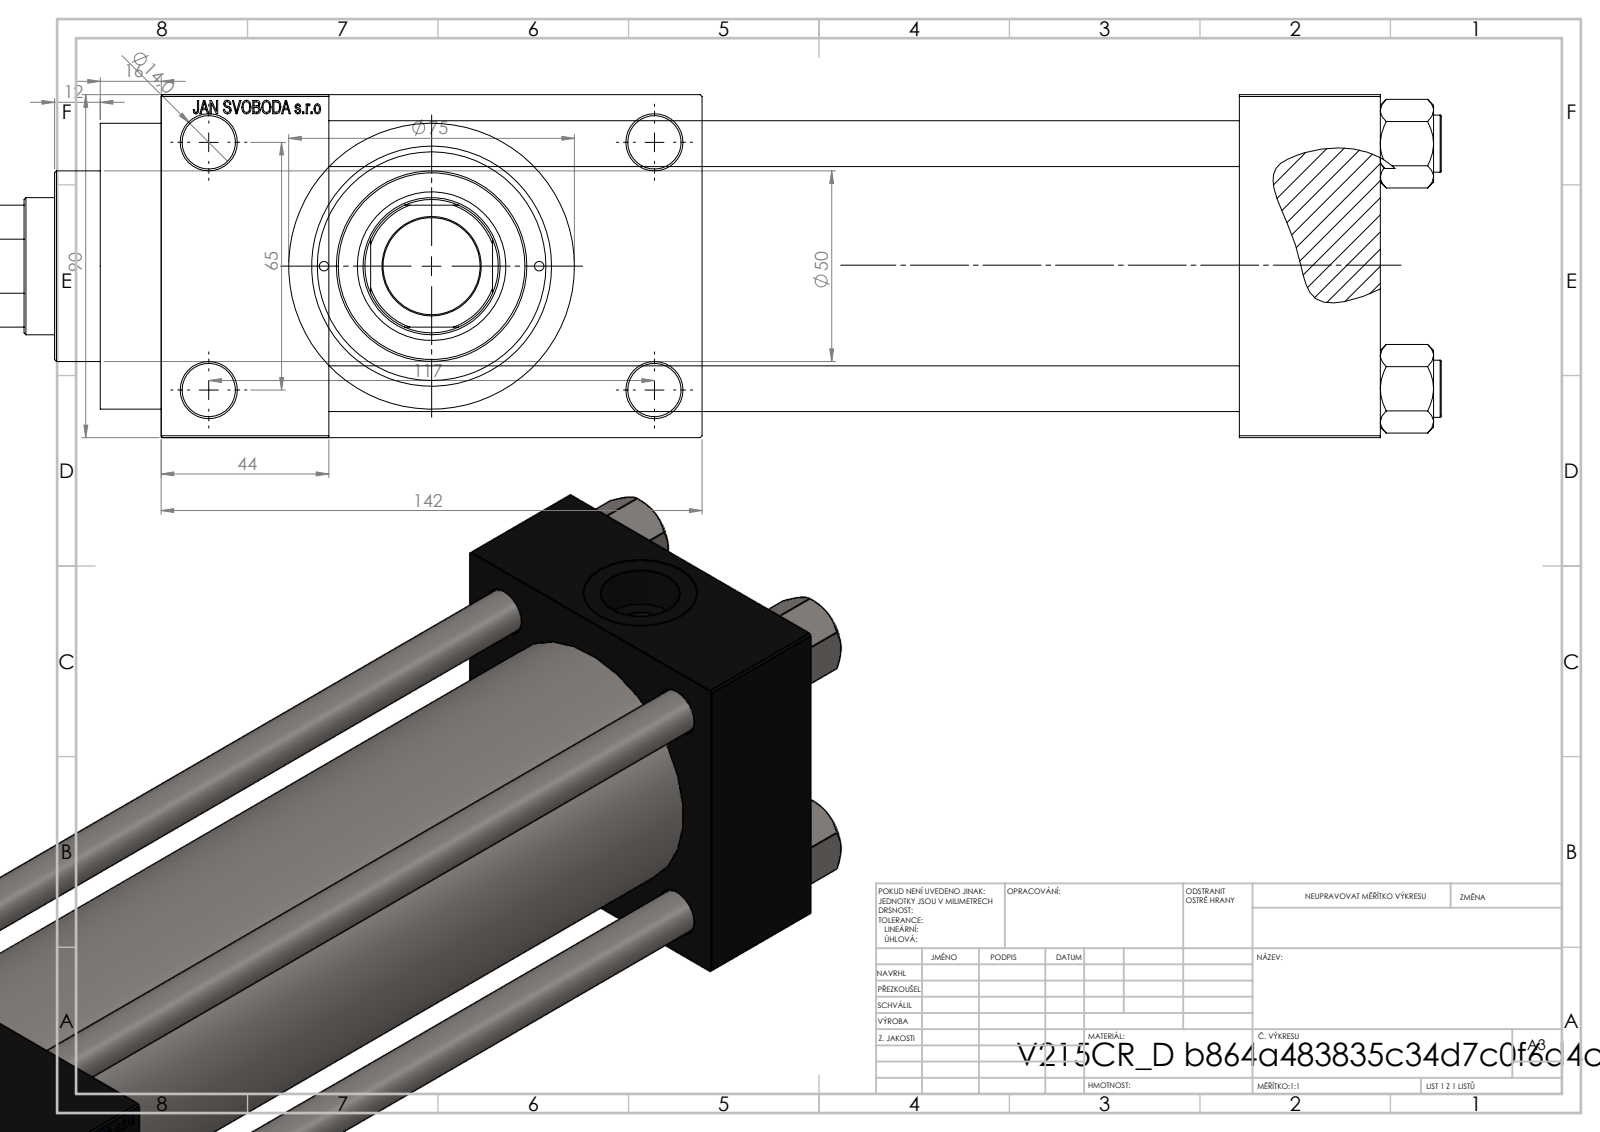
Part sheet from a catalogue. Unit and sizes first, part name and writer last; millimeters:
Units: millimetres
Overall size (bounding box): 383 × 142 × 90
Round holes (diameter × count): ⌀12 ×4, ⌀14 ×4, ⌀2.5 ×2, ⌀7 ×2, ⌀20.96 ×2, ⌀30 ×2, ⌀25.5 ×1, ⌀36 ×1, ⌀39 ×1, ⌀50 ×1, ⌀60 ×1, ⌀63 ×1
Round bosses / shafts (diameter × count): ⌀15 ×4, ⌀75 ×1, ⌀69 ×1
Partial cylindrical surfaces — rounded edges, fillets, slot ends (radius × count): R17.5 ×1
Main face-to-face distances: 90, 239, 37, 276, 320, 283, 44, 26, 116, 142
Hole centre spacings: 26.35, 32.39, 44.4, 45.47, 64.3, 66.92, 68.42, 69.81
Volume: 1 488 000 mm³ · Surface area: 327 850 mm²
Bodies: 11 solids, 1112 faces (499 planar, 93 cylindrical, 520 other)
Part name (STEP PRODUCT): NUT_M5_D; V215_VC_A; V215CR_D_TYCINKA; V215CR_D_Body (+1 more)
STEP written by: SolidWorks 2019 (CONFIG_CONTROL_DESIGN)
